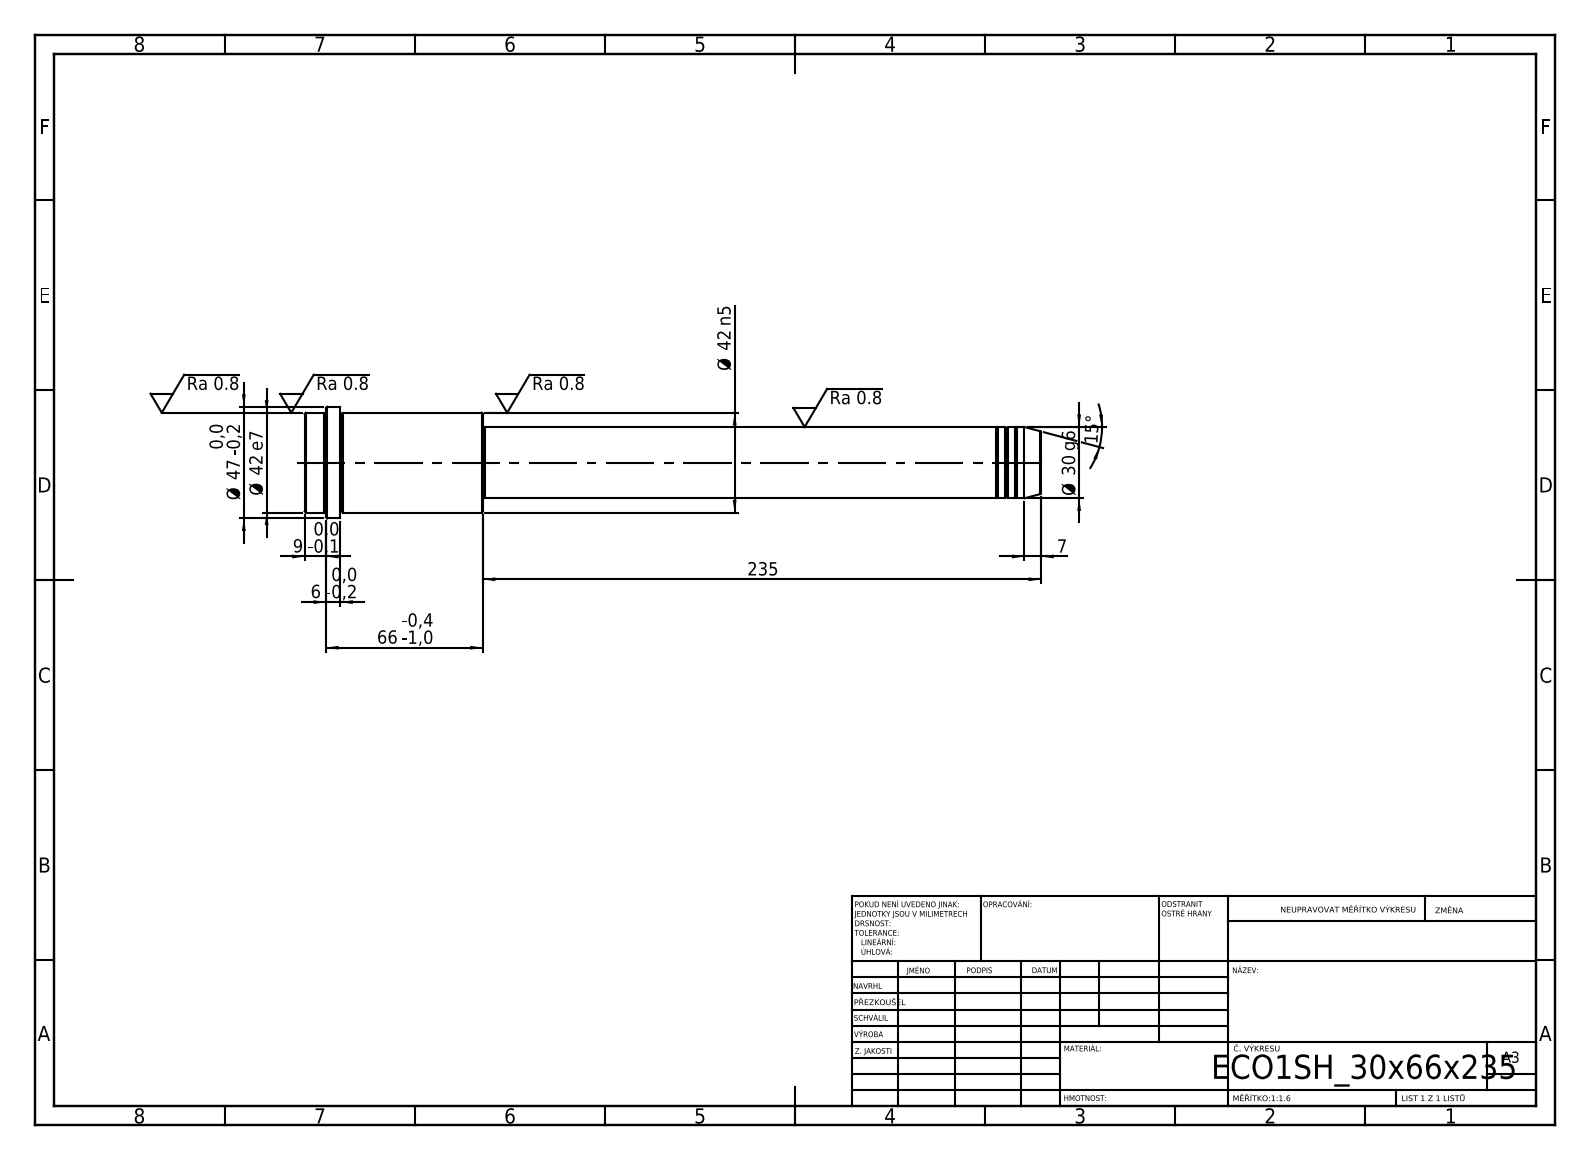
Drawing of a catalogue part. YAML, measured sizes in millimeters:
step_written_by: "SolidWorks 2019 (CONFIG_CONTROL_DESIGN)"
units: millimeters
bodies: {solids: 1, faces: 52, planar: 6, cylindrical: 16, other: 30}
overall_size: [310, 47, 47]
volume: 271212
surface_area: 35678
round_bosses_or_shafts:
  - {diameter: 47, count: 1}
  - {diameter: 42, count: 1}
  - {diameter: 30, count: 1}
  - {diameter: 29, count: 1}
face_to_face_distances: [75, 235, 310, 295, 60, 15, 301, 66, 6, 9]
